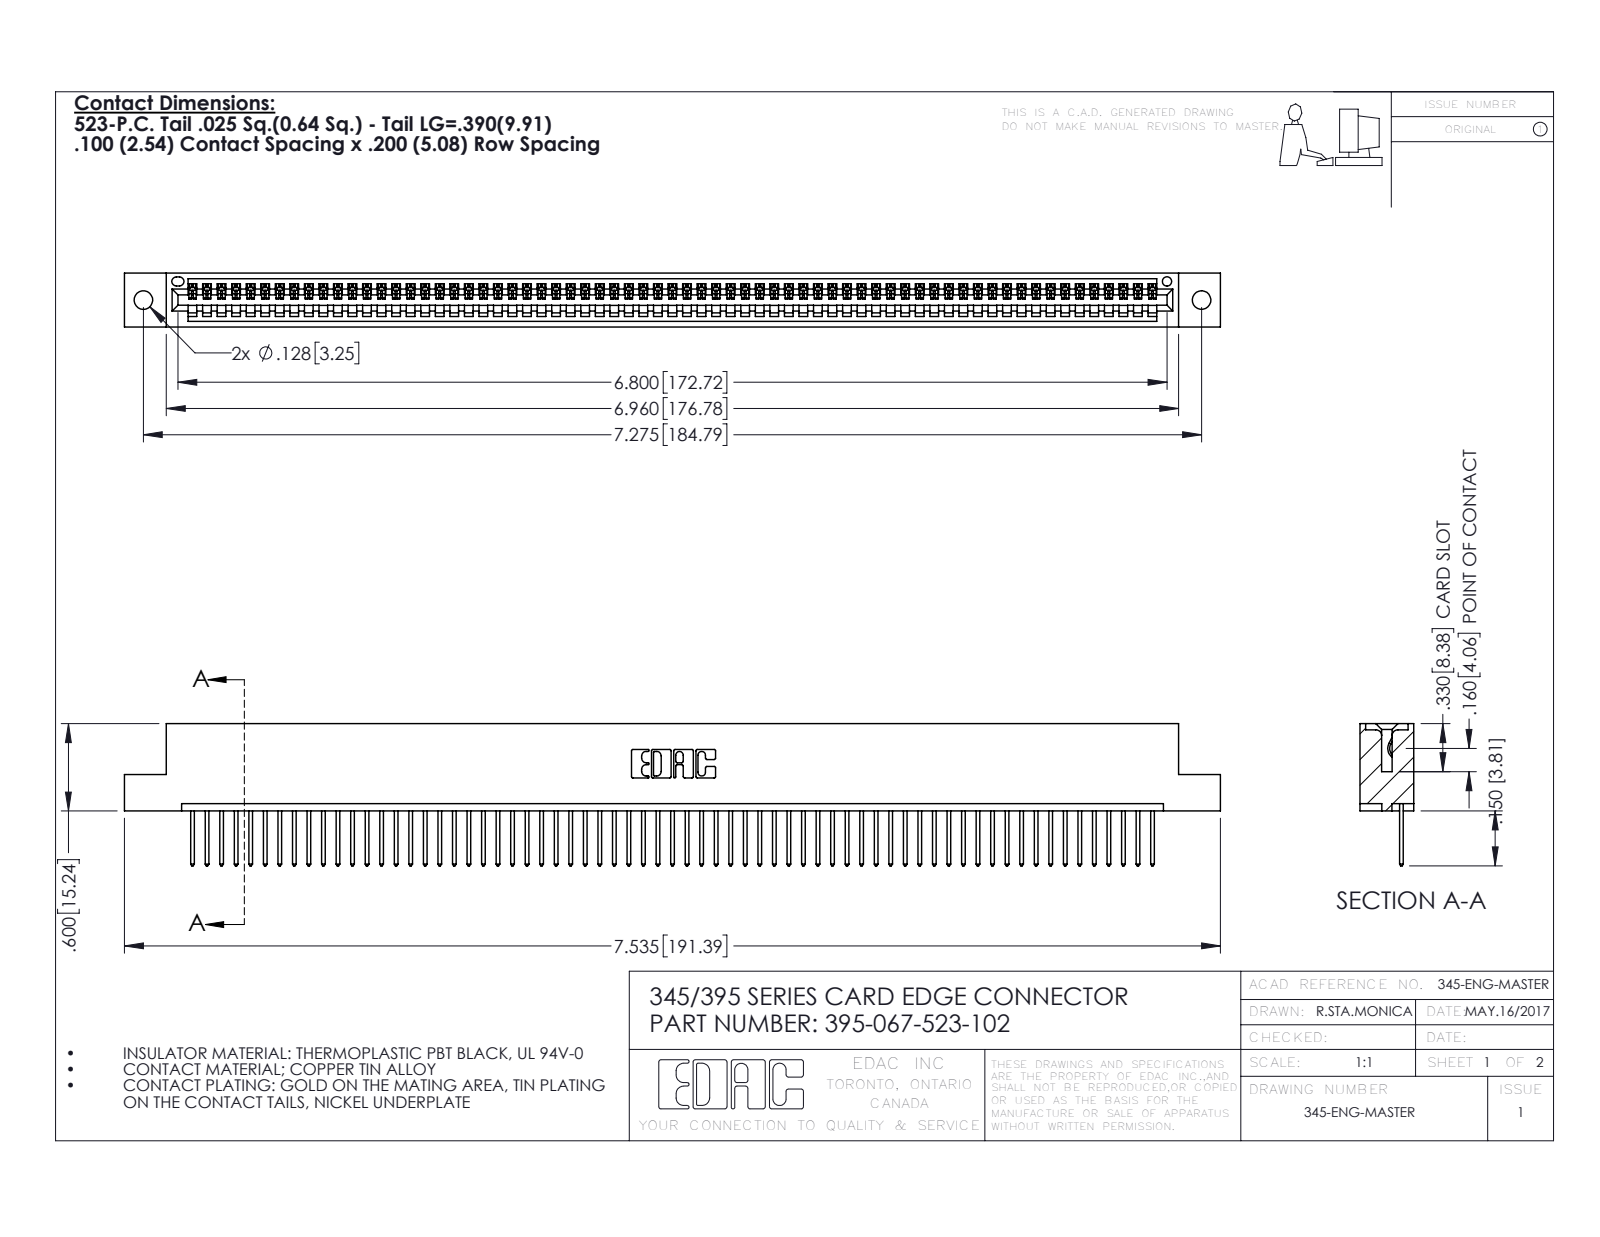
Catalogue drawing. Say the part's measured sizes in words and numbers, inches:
The part is named "395-067-523-102; 345 Part_Flush Mounting Lugs - 0.128 Dia; 345-292-001_345-293-123". Its 3-D file was written by "SolidWorks 2016 (CONFIG_CONTROL_DESIGN)". It is 68 solids with 4012 faces: 2760 planar, 1252 cylindrical and 0 other. Overall it measures 7.535 by 0.977 by 0.37 inches. Its volume is 1.118 cubic inches and its surface area 37.96 square inches. Round holes: 2 of diameter 0.128, 1 of diameter 0.064. Partial cylindrical surfaces (rounded edges, fillets, slot ends): 134 of radius 0.006, 134 of radius 0.01, 22 of radius 0.01, 6 of radius 0.007, 6 of radius 0.031, 3 of radius 0.026, 2 of radius 0.031, 2 of radius 0.04. The main face-to-face distances are 0.298, 0.072, 0.37, 0.2, 0.098, 0.272, 0.025, 0.225, 0.149, 0.072. The hole center spacings are 0.27, 7.039, 7.275.
